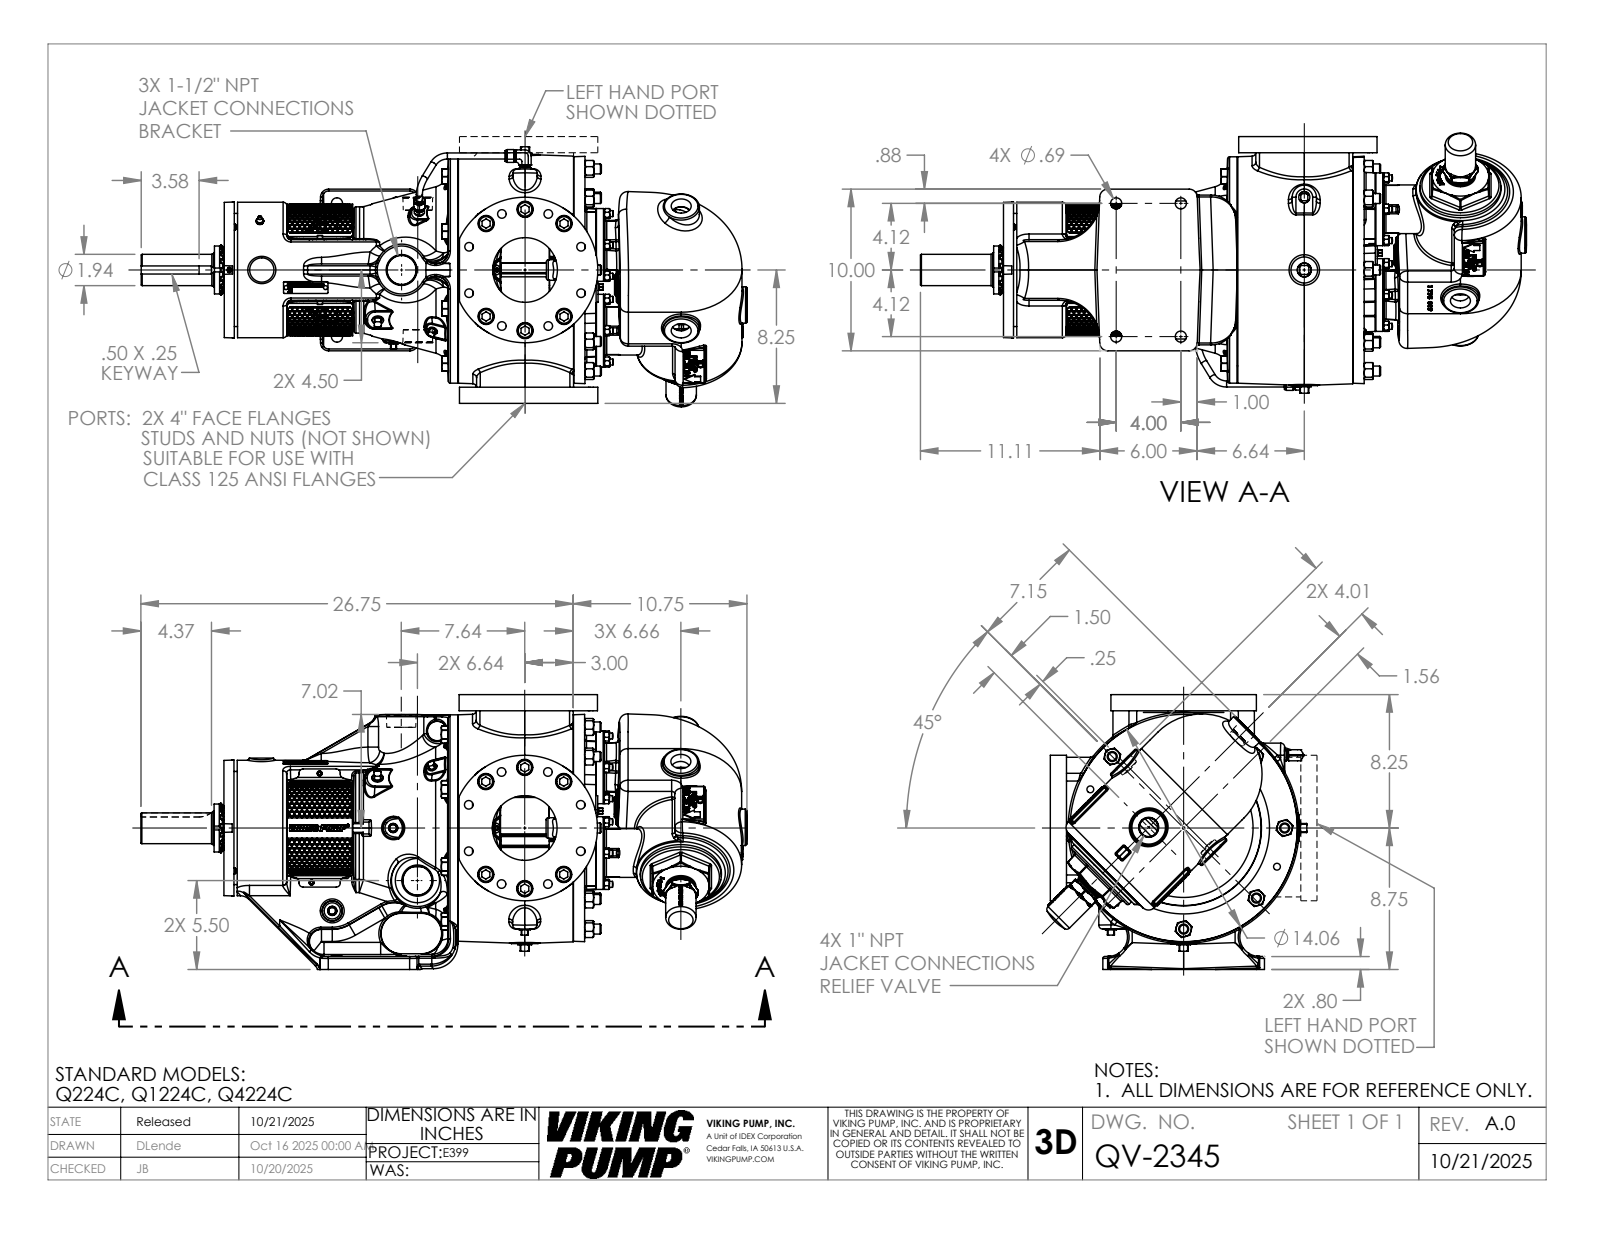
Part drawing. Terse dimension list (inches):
name: QV-2345
written by: SolidWorks 2024 (AUTOMOTIVE_DESIGN)
unit: in
bodies: 1 solid, 5167 faces (1705 planar, 814 cylindrical, 2648 other)
size: 37.499 × 17 × 16.188
volume: 2 855 in³; area: 2 546 in²
holes: 16× ⌀0.531, 13× ⌀1, 12× ⌀0.656, 9× ⌀0.25, 8× ⌀0.266, 8× ⌀1.157, 4× ⌀0.688, 2× ⌀0.159, 2× ⌀0.313, 2× ⌀0.422, 2× ⌀4, 1× ⌀0.453
bosses: 12× ⌀0.937, 9× ⌀0.625, 8× ⌀0.617, 8× ⌀0.369, 4× ⌀0.375, 3× ⌀0.625, 3× ⌀0.312, 3× ⌀0.19
rounds: 60× R0.12, 28× R0.5, 26× R0.06, 24× R0.75, 18× R0.015, 18× R0.092, 16× R0.07, 16× R0.19
face distances: 17, 22.317, 3.82, 18.498, 1, 7.972, 4.153, 14.345, 0.118, 0.882
hole spacings: 3.75, 5.303, 2.87, 6.929, 2.079, 5.783, 7.5, 1.463
